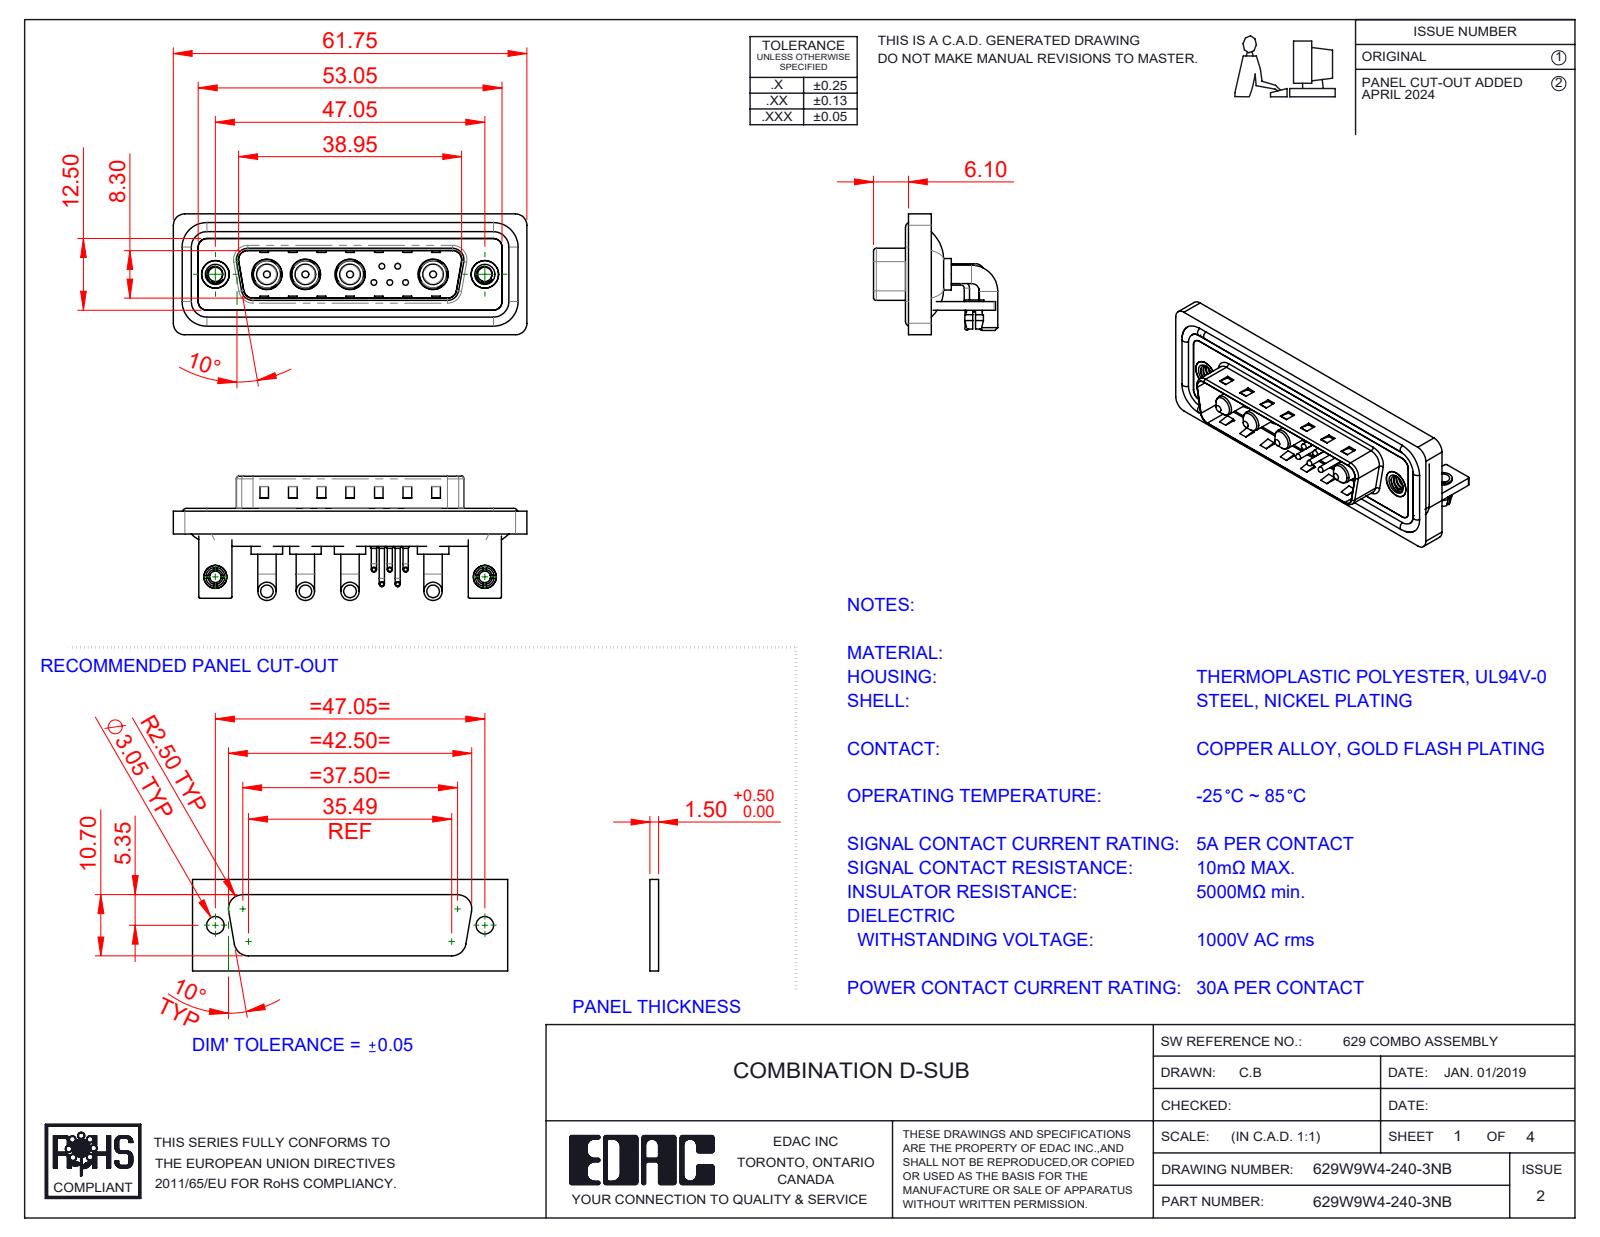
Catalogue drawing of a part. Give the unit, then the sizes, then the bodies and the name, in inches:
Units: inches
Overall size (bounding box): 2.431 × 0.854 × 0.831
Round holes (diameter × count): ⌀0.079 ×7, ⌀0.03 ×5, ⌀0.063 ×5, ⌀0.098 ×4, ⌀0.191 ×4, ⌀0.209 ×4, ⌀0.126 ×2, ⌀0.157 ×2, ⌀0.189 ×2, ⌀0.197 ×2
Round bosses / shafts (diameter × count): ⌀0.035 ×10, ⌀0.126 ×8, ⌀0.059 ×5, ⌀0.039 ×5, ⌀0.026 ×5, ⌀0.217 ×4, ⌀0.205 ×4, ⌀0.187 ×4
Partial cylindrical surfaces — rounded edges, fillets, slot ends (radius × count): R0.079 ×19, R0.059 ×18, R0.01 ×16, R0.02 ×9, R0.063 ×8, R0.04 ×5, R0.024 ×4, R0.026 ×4
Main face-to-face distances: 0.016, 0.059, 0.031, 0.114, 0.083, 0.043, 0.146, 0.161, 0.177, 0.063
Hole centre spacings: 0.124, 0.109, 0.198, 0.571, 1.852, 0.109, 0.173, 0.174
Volume: 0.496 in³ · Surface area: 20.54 in²
Bodies: 24 solids, 1335 faces (637 planar, 502 cylindrical, 196 other)
Part name (STEP PRODUCT): Power Pin_30A RA; 629Combo Shell Front_25 Contacts; 629Combo Stabilizer Bracket; 629Combo Housing_9W4 (+7 more)
STEP written by: SolidWorks 2023 (CONFIG_CONTROL_DESIGN)
